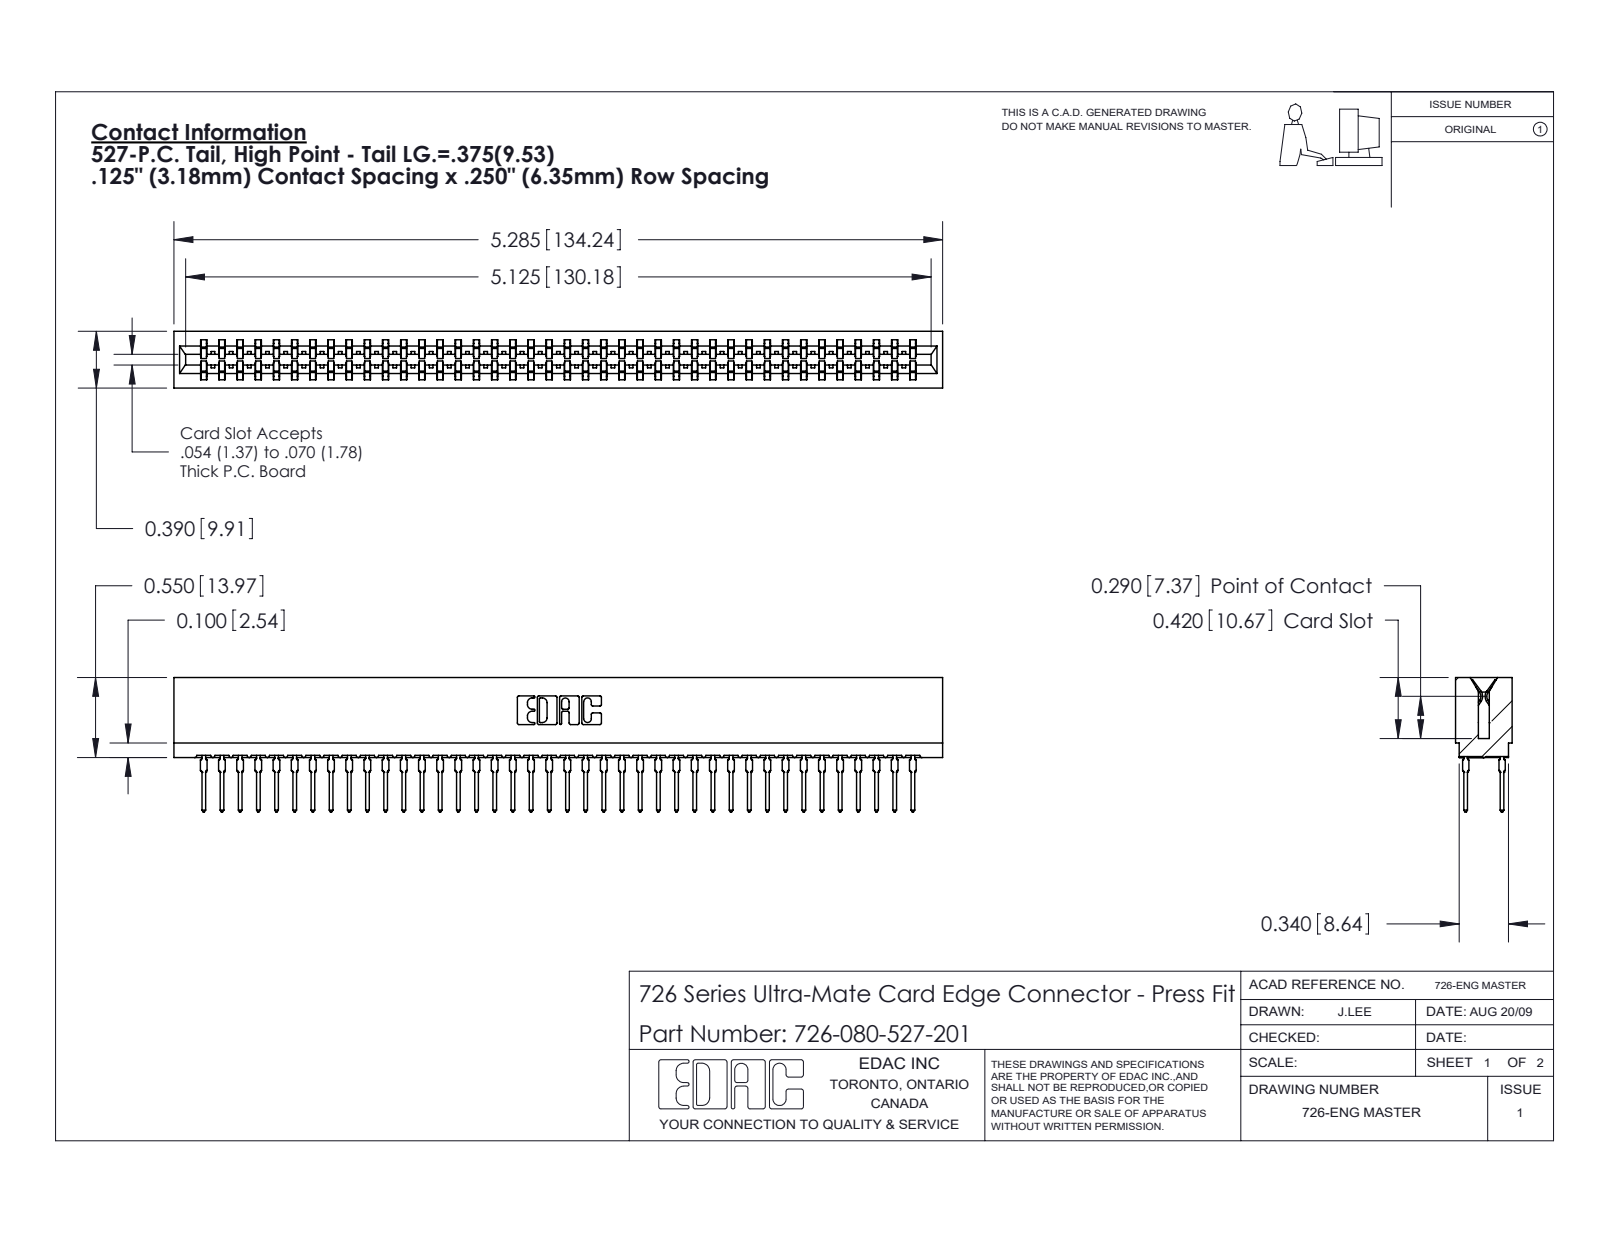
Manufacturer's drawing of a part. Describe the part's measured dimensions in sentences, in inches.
The part is named "726-080-527-201; 746-292-001_527; 726 Part_.515 Slot Depth - 01". Its 3-D file was written by "SolidWorks 2020 (CONFIG_CONTROL_DESIGN)". It is 81 solids with 7257 faces: 3735 planar, 1442 cylindrical and 2080 other. Overall it measures 5.285 by 0.924 by 0.39 inches. Its volume is 0.762 cubic inches and its surface area 33.2 square inches. Partial cylindrical surfaces (rounded edges, fillets, slot ends): 160 of radius 0.021, 41 of radius 0.015, 22 of radius 0.01, 8 of radius 0.005, 8 of radius 0.011, 6 of radius 0.007, 6 of radius 0.031, 3 of radius 0.026. The main face-to-face distances are 0.057, 0.333, 0.025, 0.25, 0.307, 0.39, 0.275, 0.083, 0.365, 0.032.
